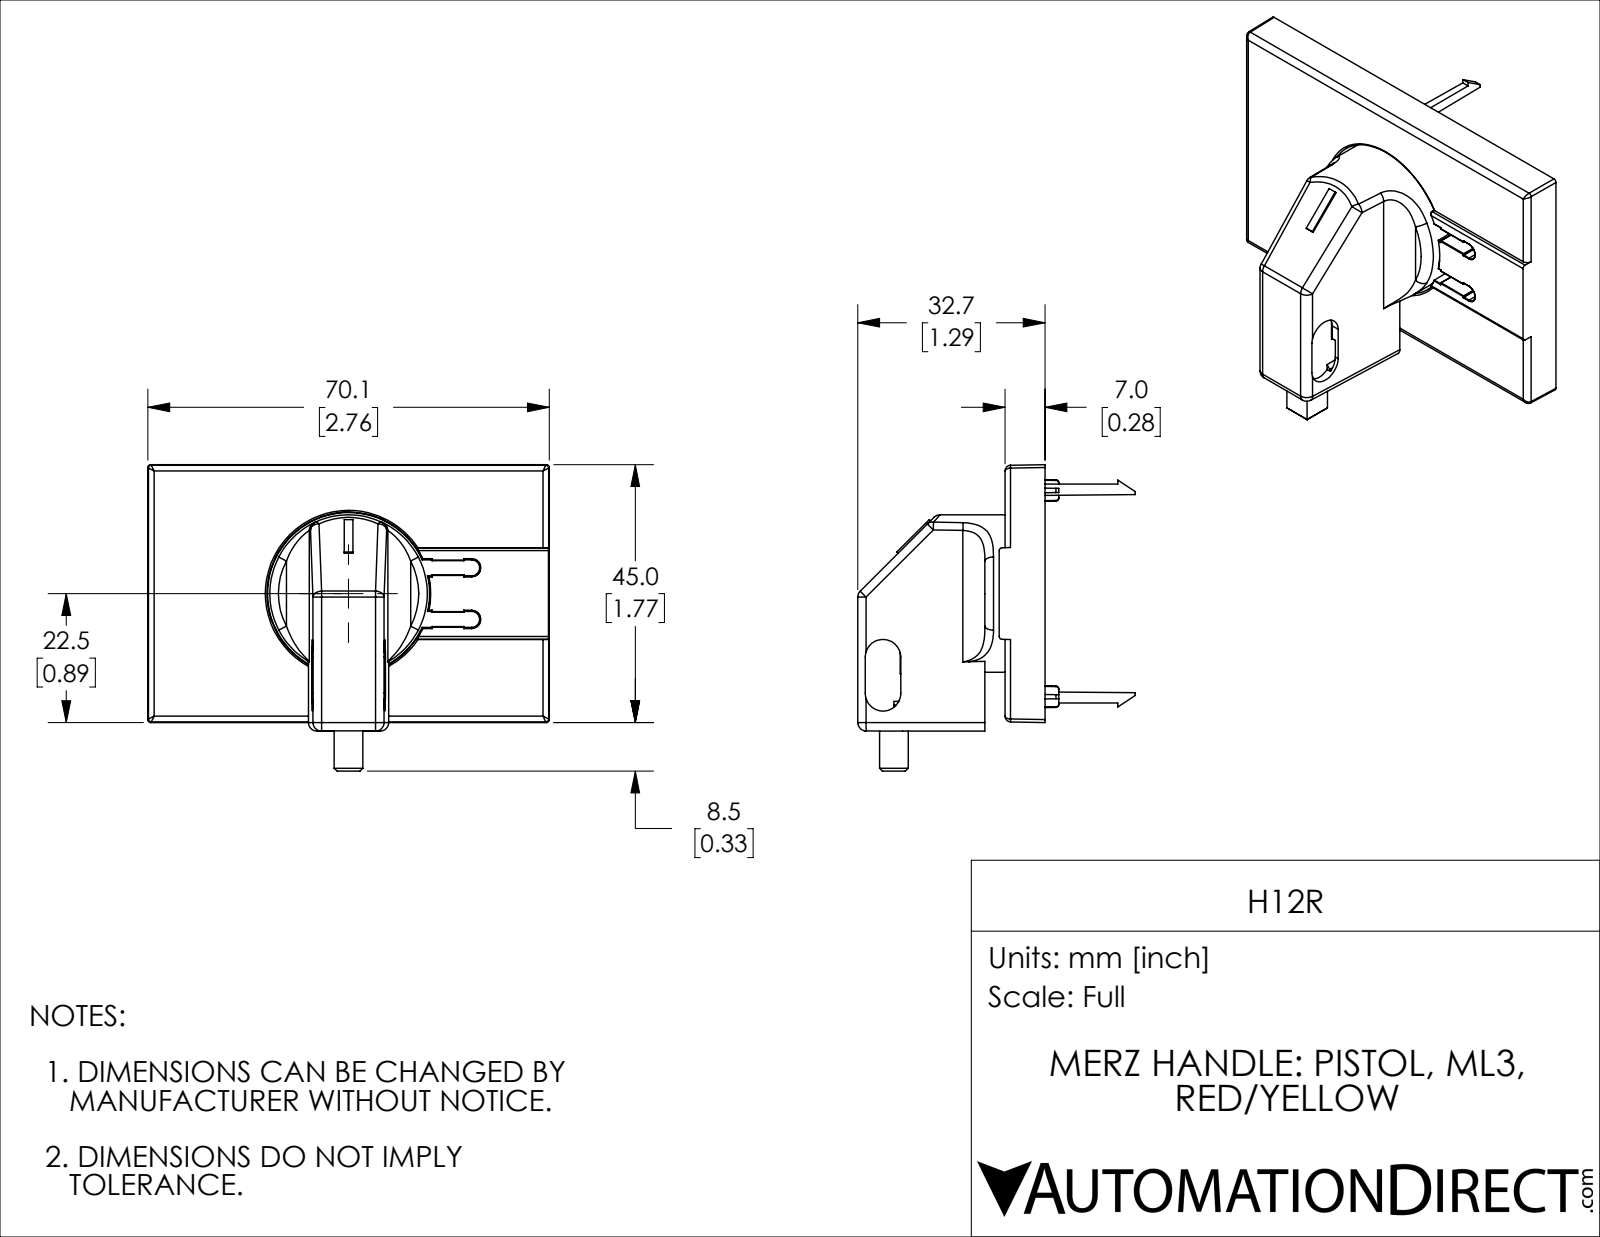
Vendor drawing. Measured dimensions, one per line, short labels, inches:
name: H12R
written by: SolidWorks 2019 (AUTOMOTIVE_DESIGN)
unit: in
bodies: 2 solids, 386 faces (212 planar, 67 cylindrical, 107 other)
size: 2.76 × 2.106 × 1.907
volume: 1.096 in³; area: 28.86 in²
bosses: 1× ⌀1.083
rounds: 18× R0.004, 8× R0.02, 8× R0.059, 5× R0.012, 4× R0.039, 2× R0.122, 2× R0.157
face distances: 0.039, 0.079, 0.197, 0.236, 0.157, 0.118, 0.276, 0.925, 0.902, 0.862
